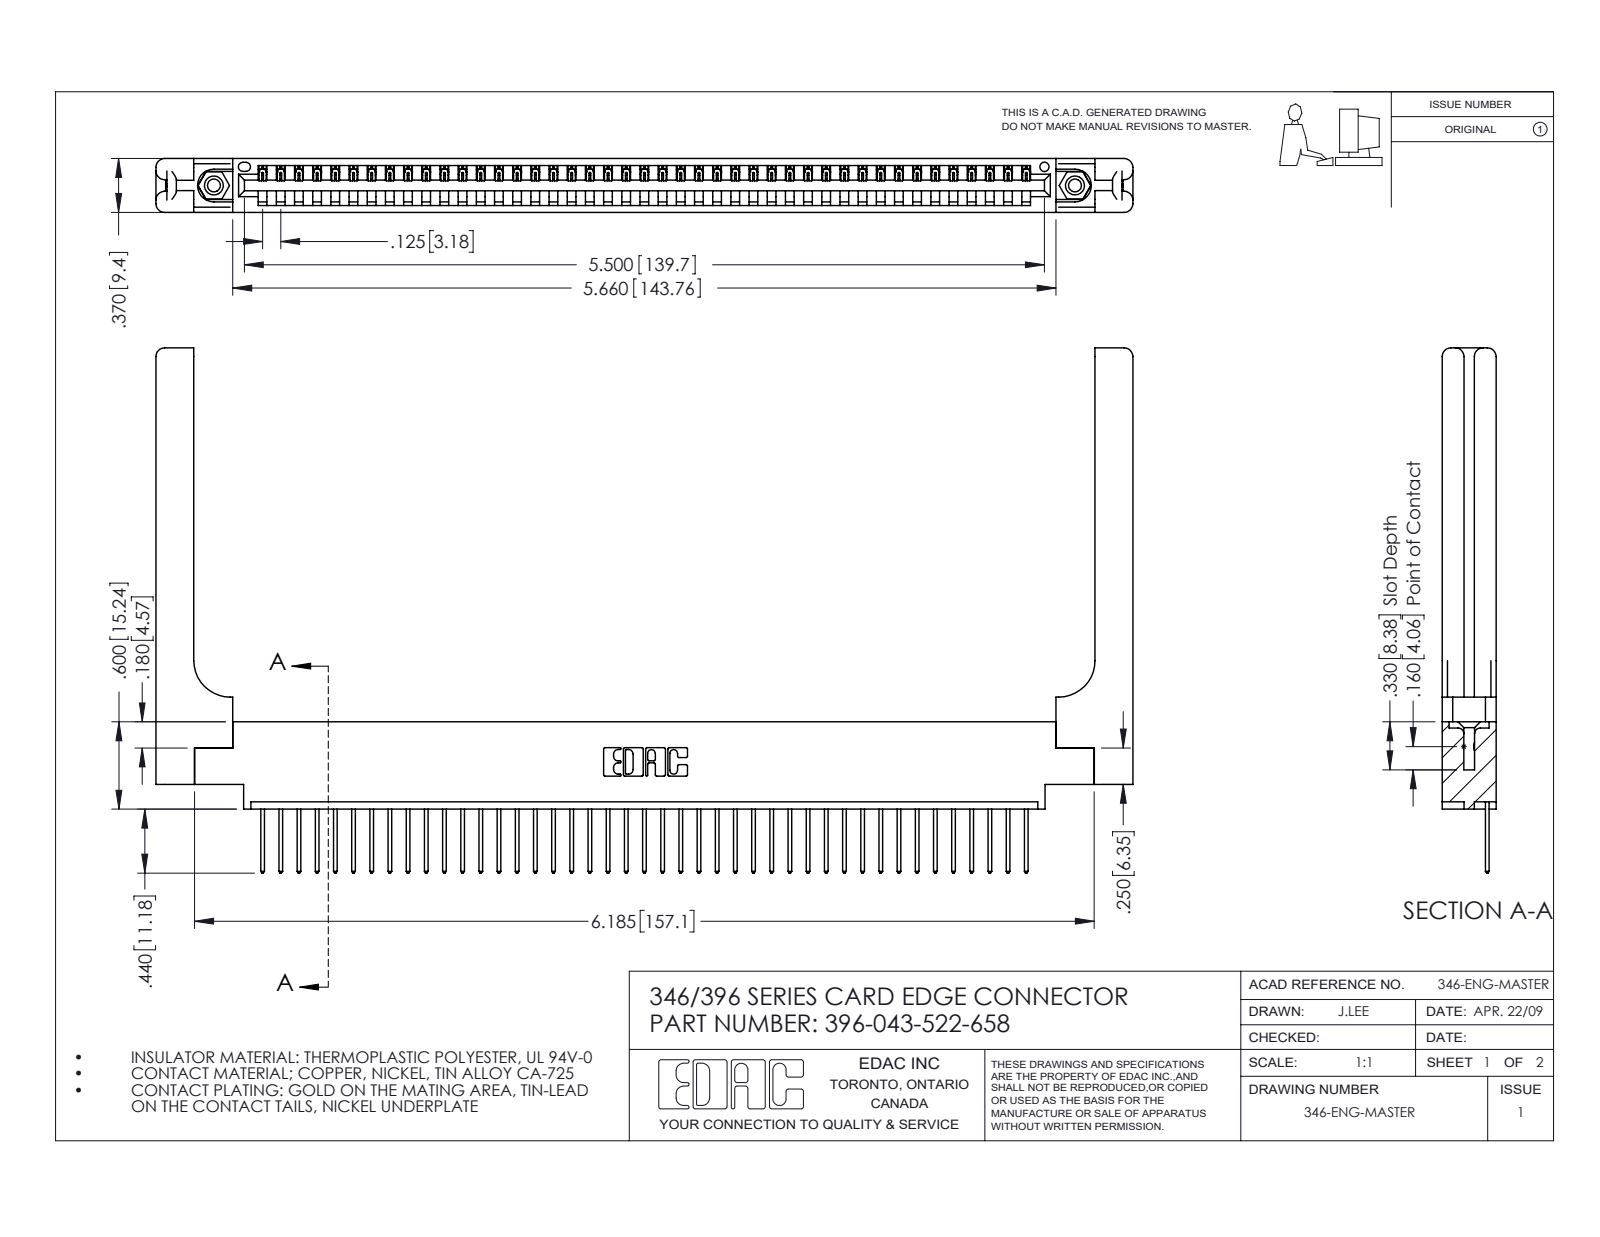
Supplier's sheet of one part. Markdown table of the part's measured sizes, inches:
| quantity | value |
| --- | --- |
| part name | 345-250-001_345-250-001-102; 345-292-001_345-293-122; 346 Part_0.170 Offset - 0.156 Dia-TH; 396-043-522-658 (+1 more) |
| STEP written by | SolidWorks 2016 (CONFIG_CONTROL_DESIGN) |
| units | inches |
| bodies | 48 solids, 2876 faces (1948 planar, 868 cylindrical, 60 other) |
| overall size | 6.716 × 3.61 × 0.37 |
| volume | 1.447 in³ |
| surface area | 39.88 in² |
| round holes (diameter × count) | 0.089 × 2, 0.125 × 2, 0.156 × 2, 0.064 × 1 |
| round bosses / shafts (diameter × count) | 0.155 × 2 |
| partial cylindrical surfaces (radius × count) | 0.006 × 86, 0.01 × 86, 0.01 × 22, 0.06 × 16, 0.007 × 6, 0.031 × 6, 0.026 × 3, 0.03 × 2 |
| main face-to-face distances | 0.37, 0.048, 0.322, 0.072, 0.148, 0.15, 0.25, 0.298, 0.025, 0.222 |
| hole center spacings | 0.246, 5.711, 5.92 |
